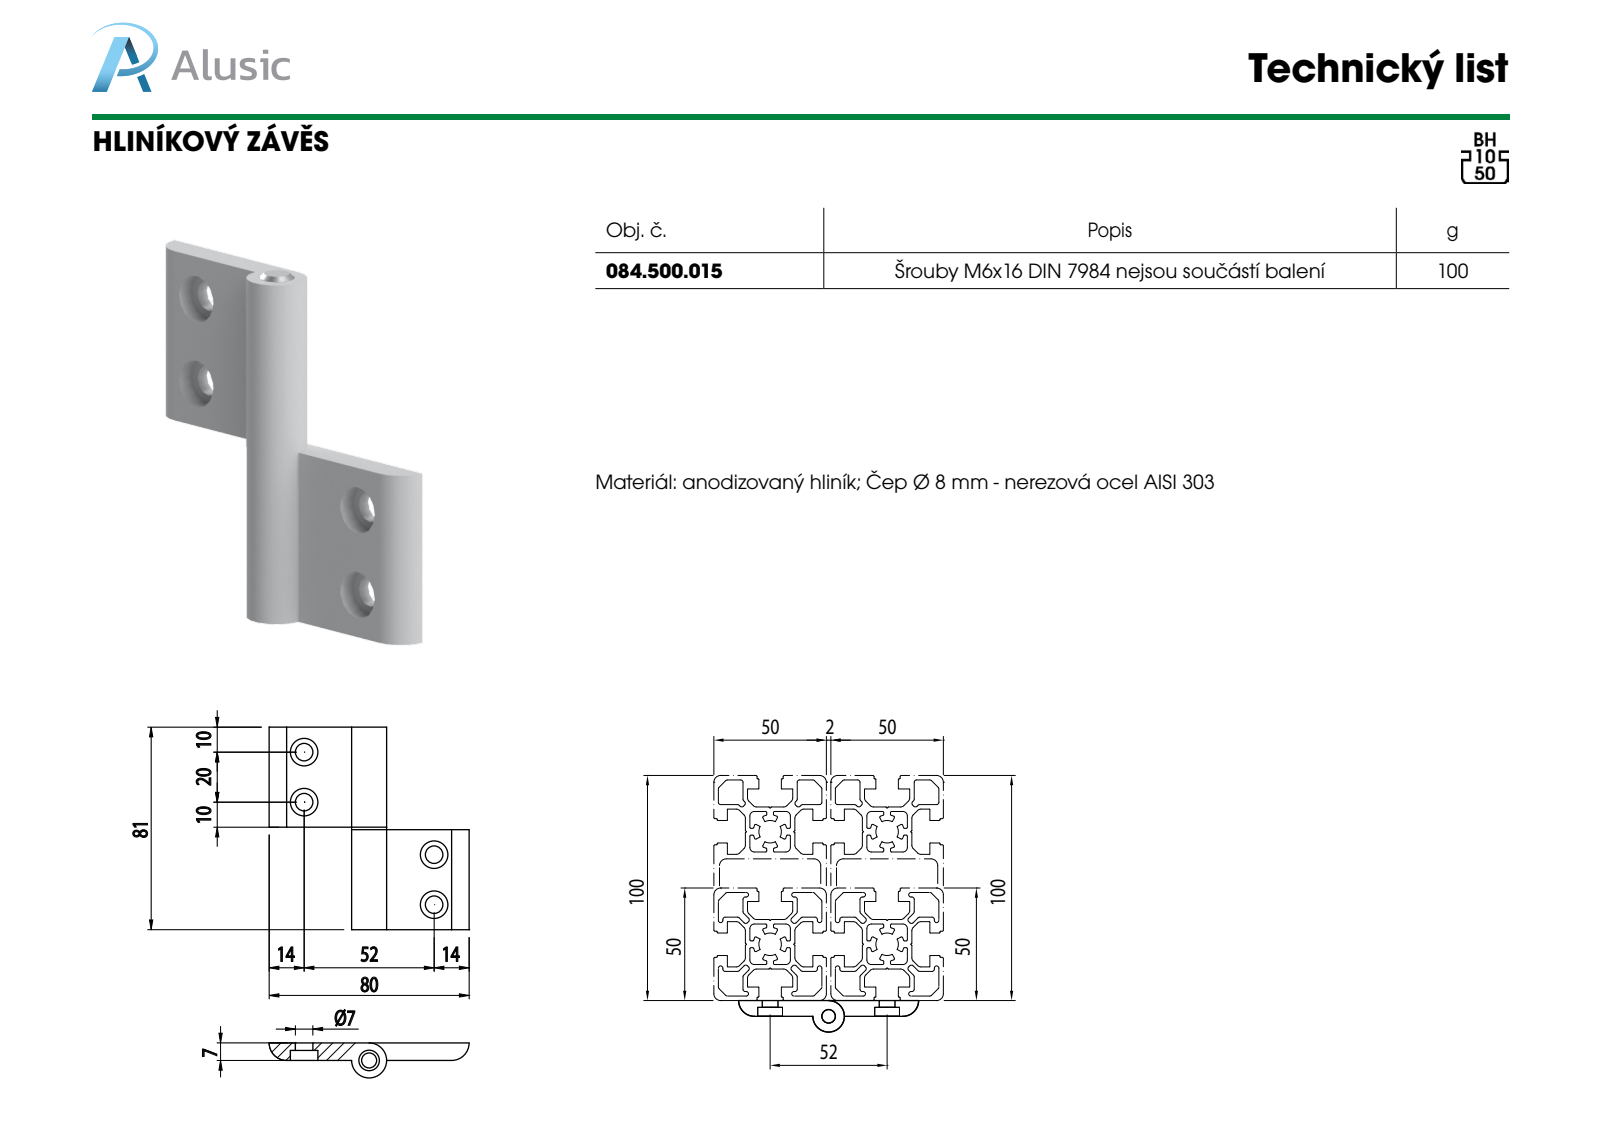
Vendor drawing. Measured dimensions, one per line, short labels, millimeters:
name: 084.500.015; PERNO CERNIERA_084.500.001.B; SEMI CERNIERA_084.500.015A
written by: SolidWorks 2012 (CONFIG_CONTROL_DESIGN)
unit: mm
bodies: 3 solids, 166 faces (134 planar, 28 cylindrical, 4 other)
size: 81 × 81 × 14
volume: 28 908 mm³; area: 14 935 mm²
holes: 4× ⌀7, 4× ⌀11, 1× ⌀8.2
bosses: 1× ⌀14, 1× ⌀8
rounds: 2× R7
face distances: 7, 40, 80, 3, 4, 6.11, 81, 41, 1, 6.12
hole spacings: 20, 65.6, 55.71, 79.4
